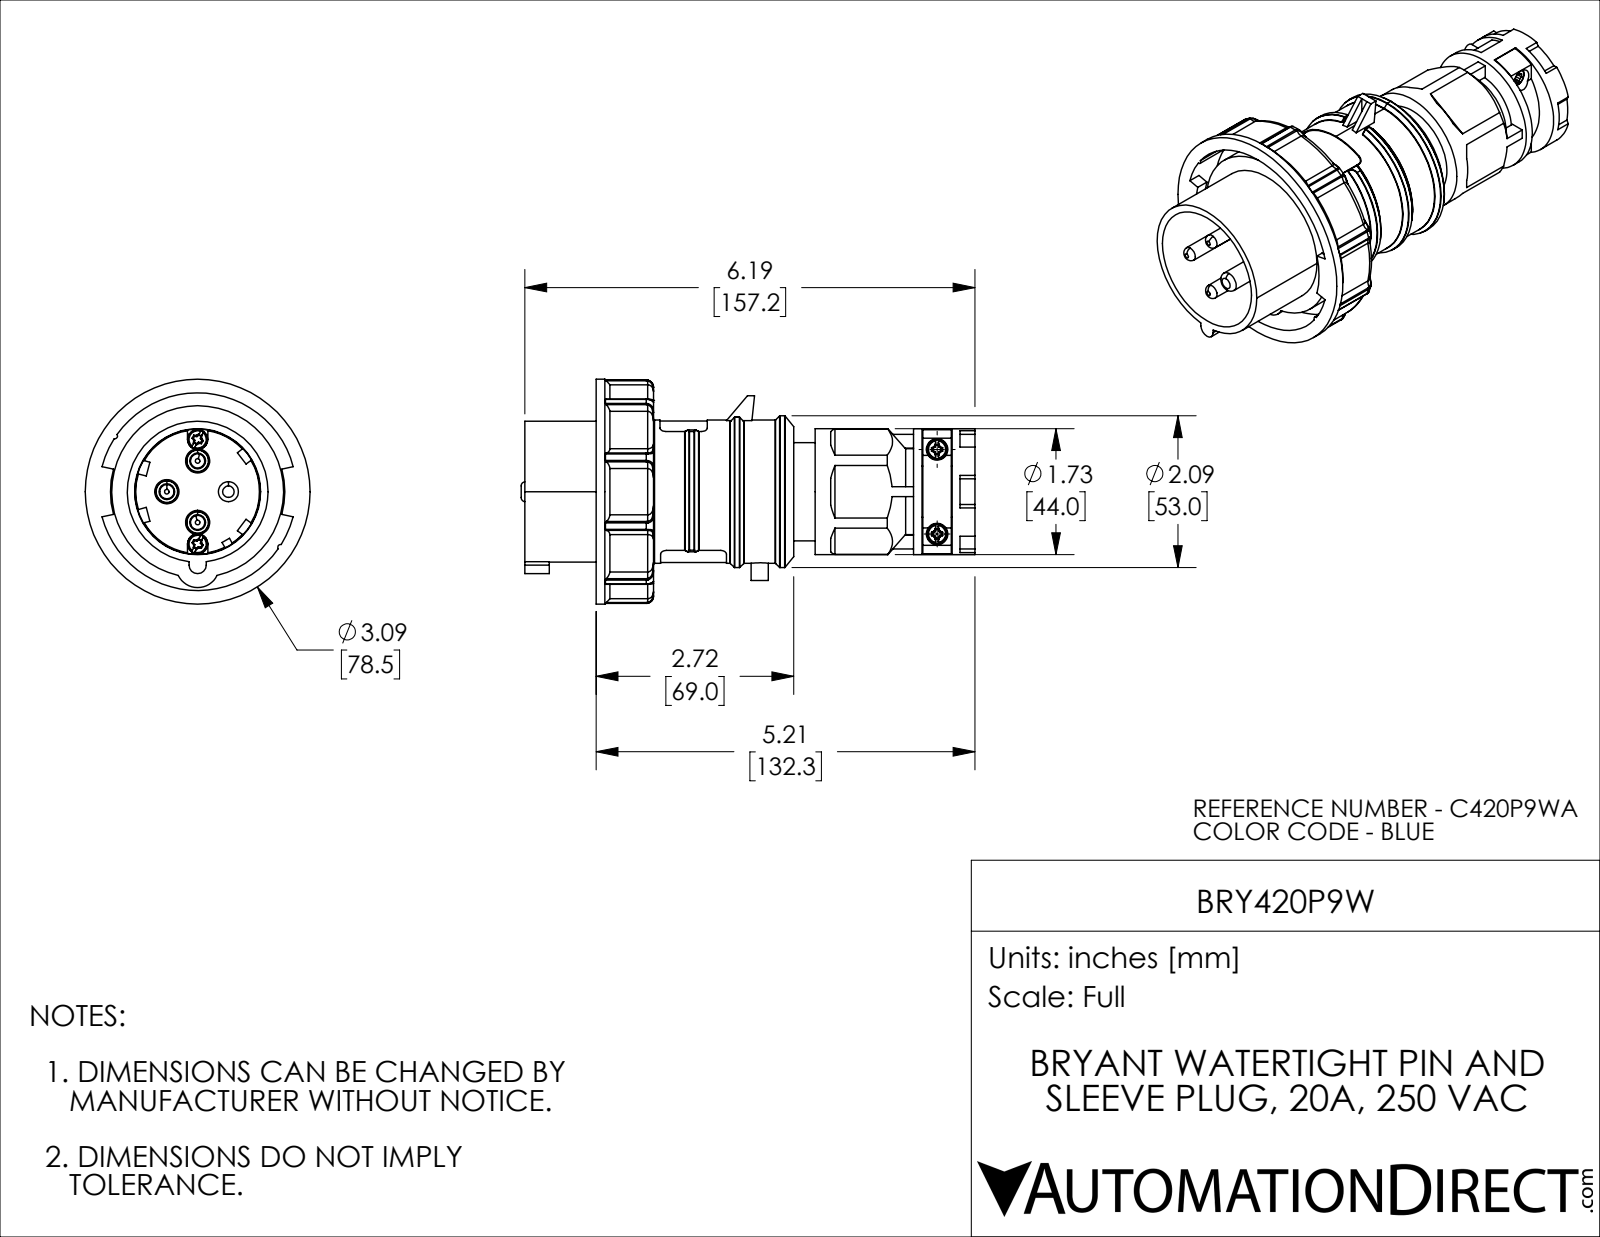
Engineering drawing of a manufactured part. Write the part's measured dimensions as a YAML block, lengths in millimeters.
part_name: "BRY420P9W"
step_written_by: "SolidWorks 2021 (CONFIG_CONTROL_DESIGN)"
units: millimeters
bodies: {solids: 9, faces: 741, planar: 260, cylindrical: 237, other: 244}
overall_size: [158.5, 78.5, 78.5]
volume: 228046
surface_area: 68431
round_holes:
  - {diameter: 4, count: 2}
  - {diameter: 7.5, count: 2}
  - {diameter: 3.1, count: 1}
  - {diameter: 37.38, count: 1}
  - {diameter: 49.2, count: 1}
  - {diameter: 50.6, count: 1}
  - {diameter: 69, count: 1}
round_bosses_or_shafts:
  - {diameter: 5, count: 3}
  - {diameter: 78.5, count: 1}
  - {diameter: 60, count: 1}
  - {diameter: 53, count: 1}
  - {diameter: 50, count: 1}
  - {diameter: 47.7, count: 1}
  - {diameter: 44, count: 1}
  - {diameter: 34.29, count: 1}
partial_cylinders:
  - {radius: 2.5, count: 26}
  - {radius: 0.5, count: 20}
  - {radius: 2, count: 8}
  - {radius: 1, count: 5}
  - {radius: 0.2, count: 2}
  - {radius: 3.55, count: 2}
  - {radius: 23.5, count: 2}
  - {radius: 1.2, count: 1}
face_to_face_distances: [6.3, 3, 13.5, 10.25, 3.25, 13.25, 55.3, 20, 13.7, 2.1]
hole_center_spacings: [29.5]
